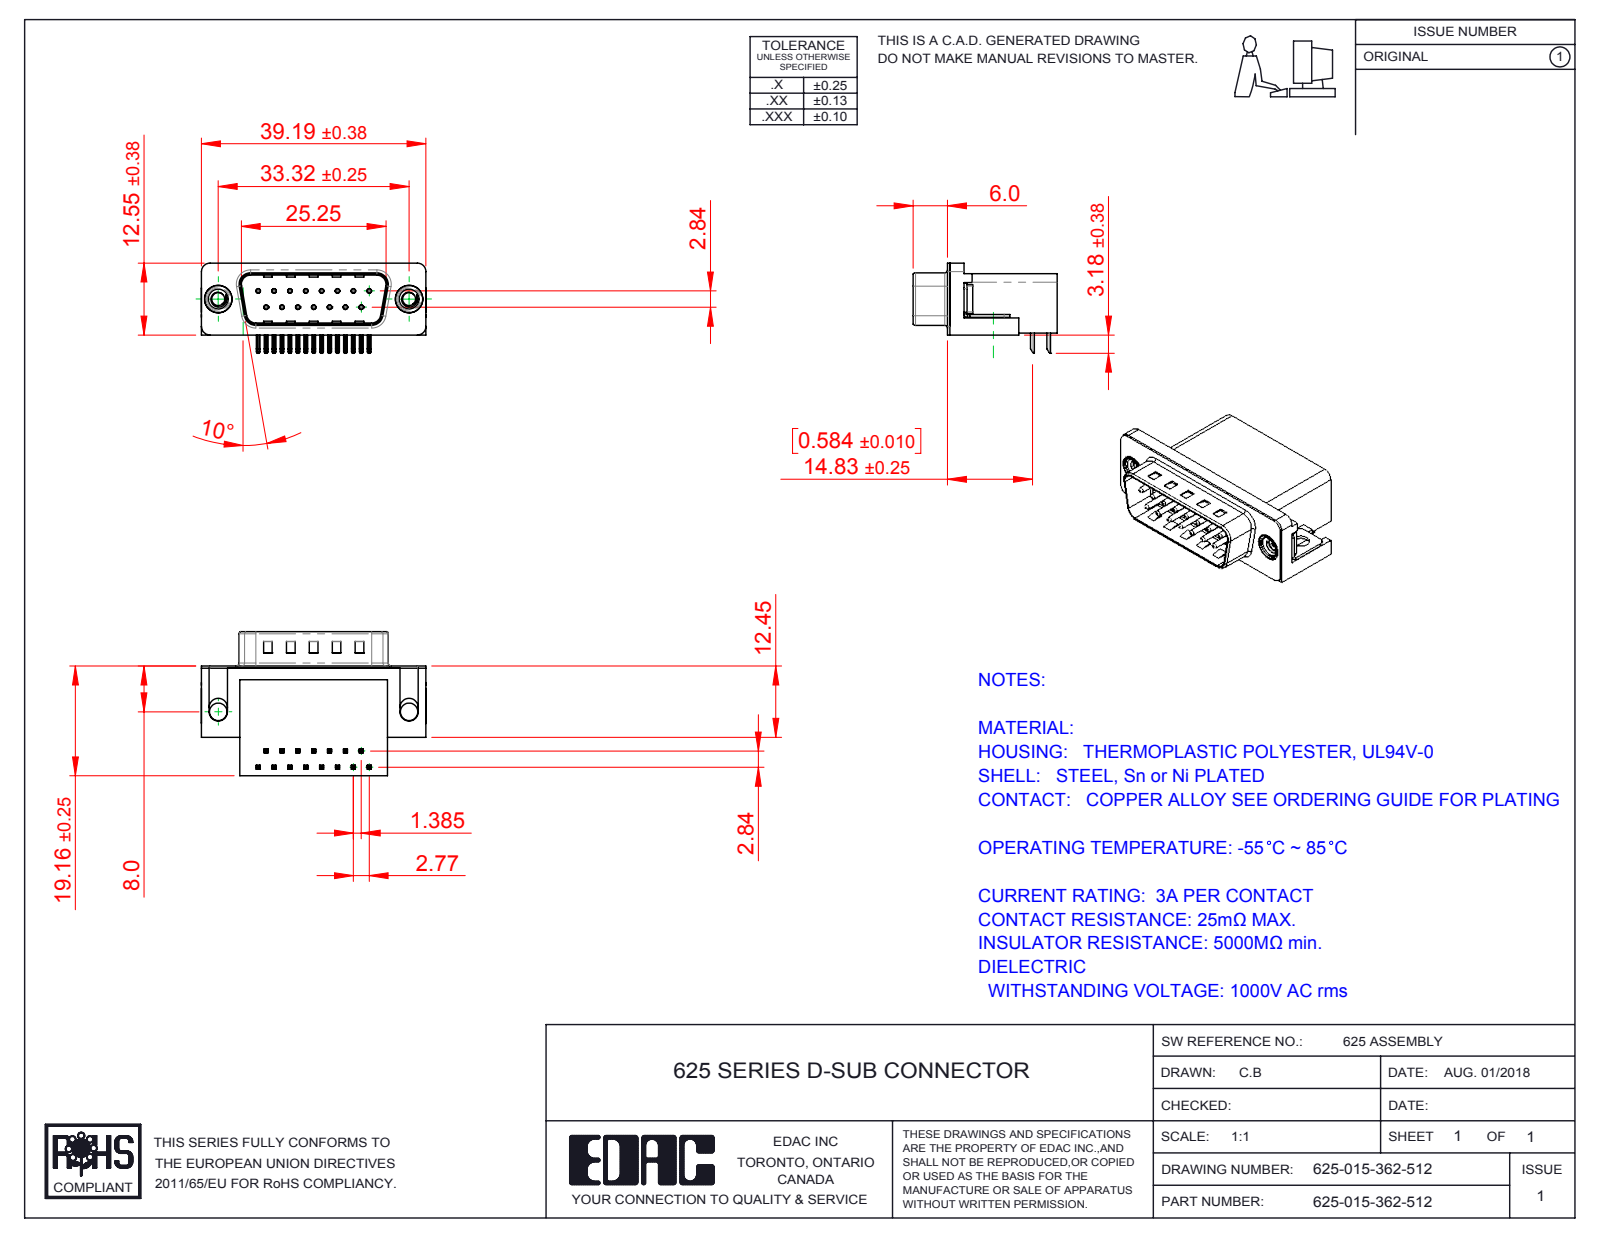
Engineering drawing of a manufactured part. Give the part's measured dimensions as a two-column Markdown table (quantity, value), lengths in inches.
| quantity | value |
| --- | --- |
| part name | 625 Shell_15 Socket; 625 4-40 Threaded Rivet; 625-015-362-512; 625 Thru Hole Board Mount (+3 more) |
| STEP written by | SolidWorks 2016 (CONFIG_CONTROL_DESIGN) |
| units | inches |
| bodies | 21 solids, 1479 faces (893 planar, 447 cylindrical, 139 other) |
| overall size | 1.544 × 0.991 × 0.619 |
| volume | 0.381 in³ |
| surface area | 9.939 in² |
| round holes (diameter × count) | 0.014 × 15, 0.031 × 15, 0.089 × 2, 0.12 × 2, 0.157 × 2, 0.189 × 2, 0.197 × 2 |
| round bosses / shafts (diameter × count) | 0.03 × 15, 0.193 × 2, 0.187 × 2, 0.154 × 2 |
| partial cylindrical surfaces (radius × count) | 0.01 × 68, 0.005 × 30, 0.039 × 16, 0.02 × 9, 0.063 × 8, 0.059 × 6, 0.035 × 4, 0.079 × 4 |
| main face-to-face distances | 0.016, 0.407, 0.739, 0.083, 0.412, 0.754, 0.067, 0.428, 0.345, 0.64 |
| hole center spacings | 0.124, 0.109, 0.218, 0.327, 0.436, 0.198, 0.198, 0.294 |
